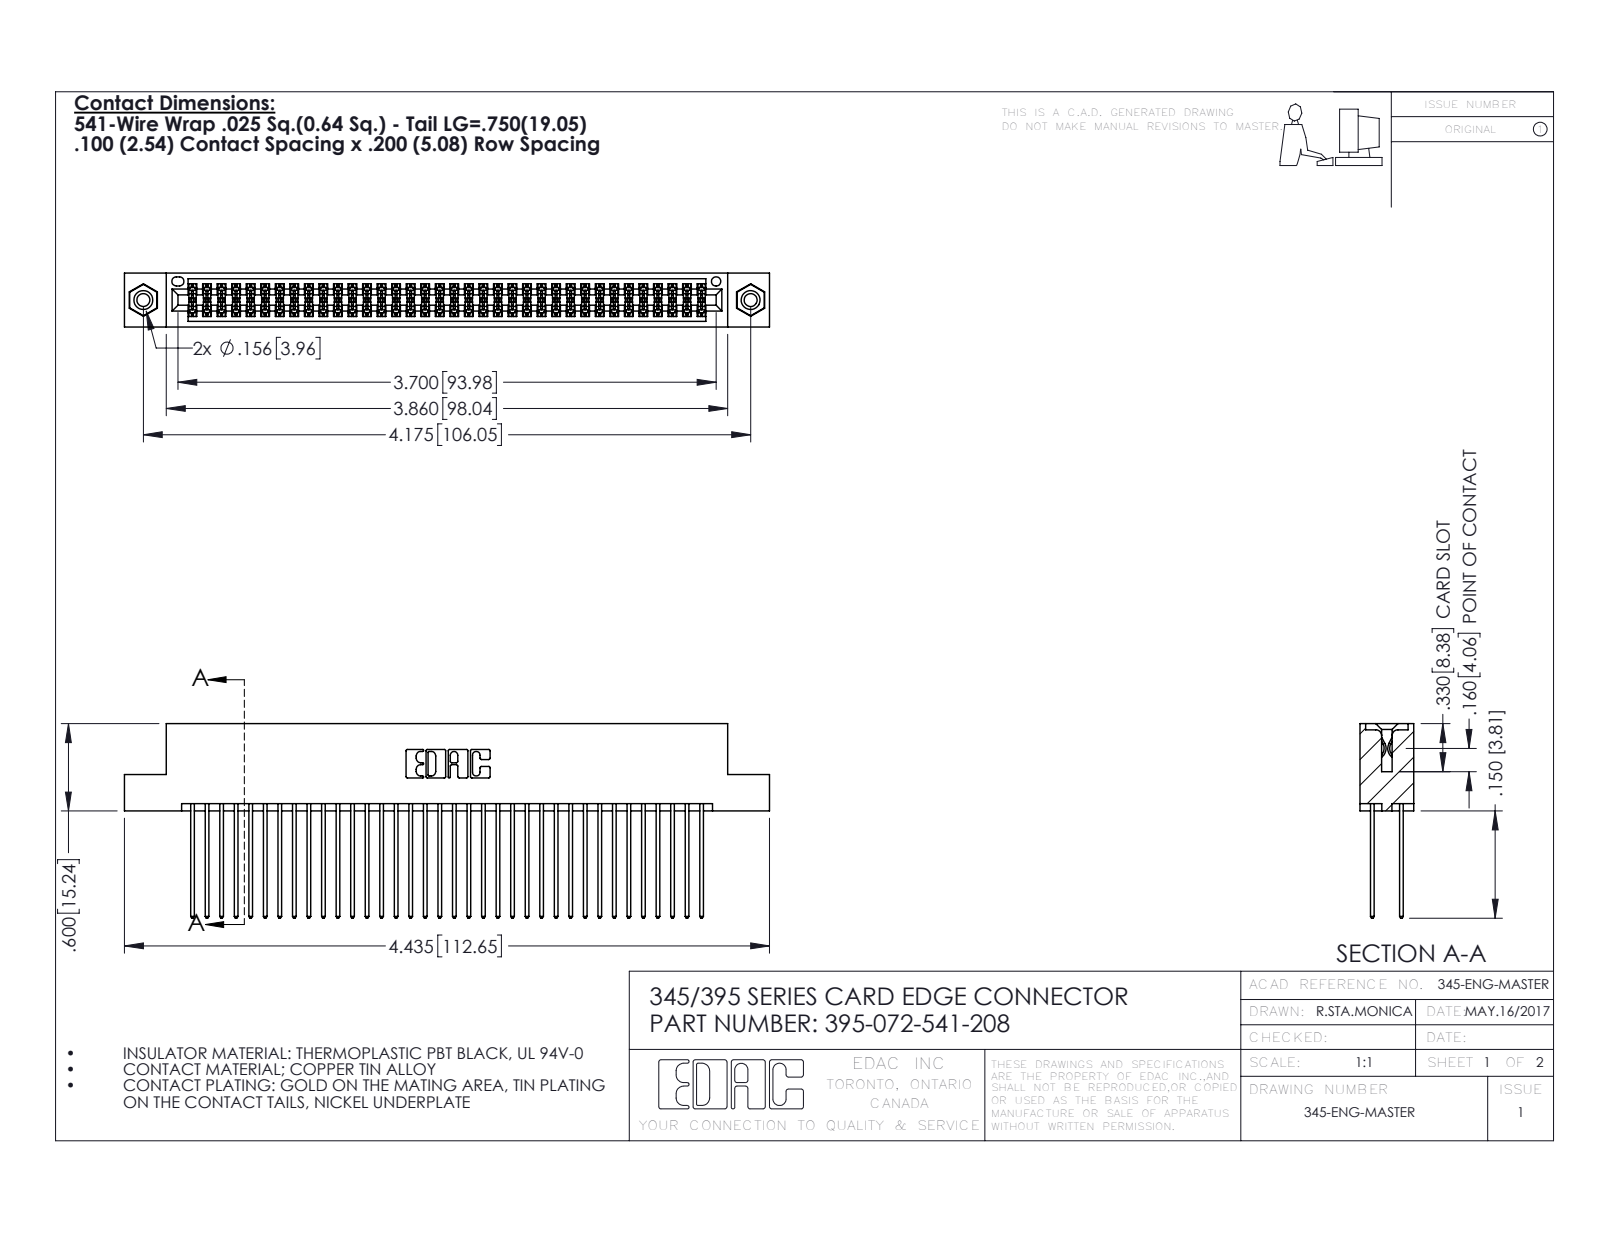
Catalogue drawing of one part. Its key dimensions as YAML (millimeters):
part_name: "345-250-001_345-250-003-102; 345 Part_Flush Mounting Lugs - 0.156 Dia-TI; 345-292-001_345-293-141; 395-072-541-208"
step_written_by: "SolidWorks 2016 (CONFIG_CONTROL_DESIGN)"
units: millimeters
bodies: {solids: 75, faces: 3786, planar: 2488, cylindrical: 1282, other: 16}
overall_size: [112.6, 34, 9.4]
volume: 11300
surface_area: 18540
round_holes:
  - {diameter: 2.3, count: 2}
  - {diameter: 3.2, count: 2}
  - {diameter: 4, count: 2}
  - {diameter: 1.6, count: 1}
round_bosses_or_shafts:
  - {diameter: 3.9, count: 2}
partial_cylinders:
  - {radius: 0.2, count: 108}
  - {radius: 0.3, count: 72}
  - {radius: 0.3, count: 22}
  - {radius: 0.2, count: 6}
  - {radius: 0.8, count: 6}
  - {radius: 0.7, count: 3}
  - {radius: 0.4, count: 2}
  - {radius: 0.5, count: 2}
face_to_face_distances: [1.8, 7.6, 5.1, 2.5, 6.9, 0.6, 5.7, 9.4, 4.4, 3.8]
hole_center_spacings: [6.9, 100.1, 106]
